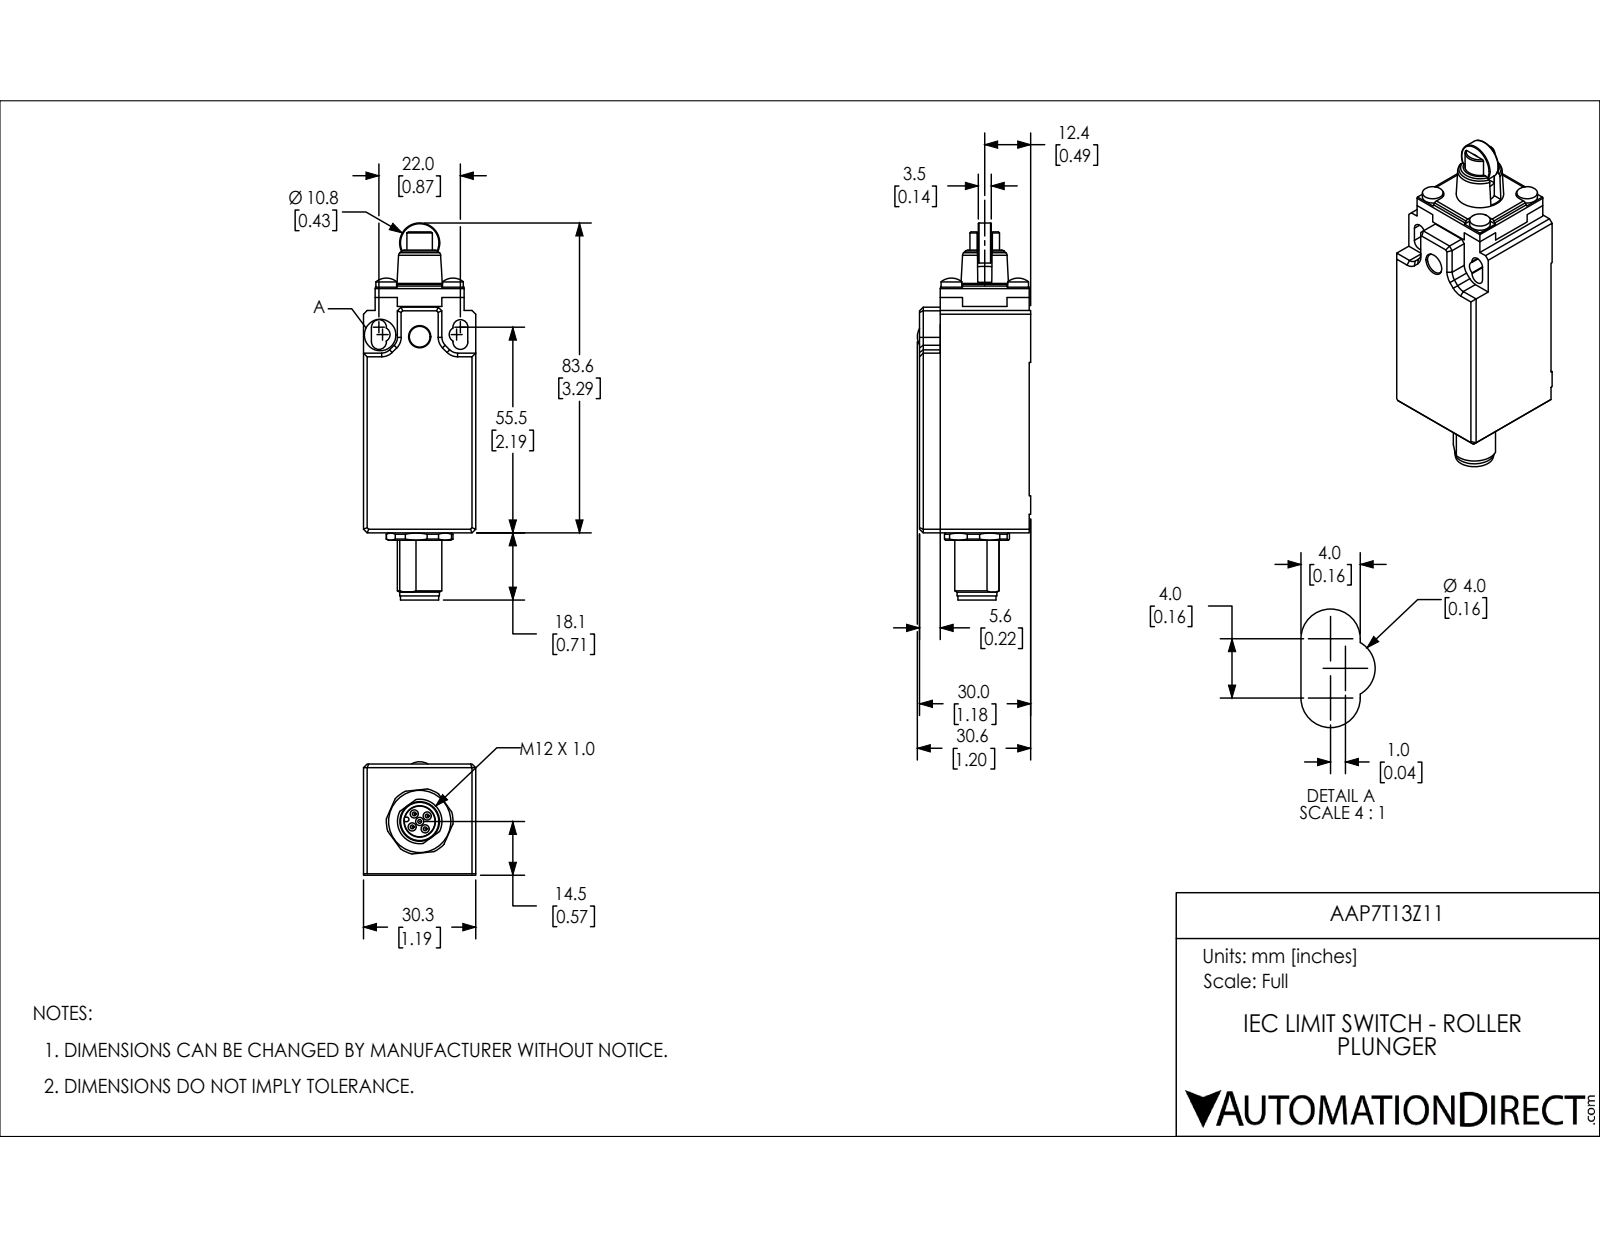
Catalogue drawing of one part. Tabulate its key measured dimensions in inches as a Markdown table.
| quantity | value |
| --- | --- |
| part name | AAP7T13Z11 |
| STEP written by | SolidWorks 2018 (AUTOMOTIVE_DESIGN) |
| units | inches |
| bodies | 5 solids, 328 faces (150 planar, 119 cylindrical, 59 other) |
| overall size | 4.004 × 1.205 × 1.193 |
| volume | 3.599 in³ |
| surface area | 25.07 in² |
| round holes (diameter × count) | 0.087 × 5, 0.236 × 1, 0.319 × 1, 0.512 × 1, 0.551 × 1, 0.63 × 1 |
| round bosses / shafts (diameter × count) | 0.22 × 6, 0.055 × 5, 0.039 × 5, 0.425 × 1, 0.421 × 1, 0.406 × 1, 0.315 × 1 |
| partial cylindrical surfaces (radius × count) | 0.039 × 8, 0.118 × 8, 0.079 × 6, 0.024 × 1, 0.236 × 1, 0.354 × 1, 0.394 × 1, 0.4 × 1 |
| main face-to-face distances | 1.193, 1.165, 2.406, 0.016, 1.181, 0.945, 0.236, 0.15, 0.039, 2.5 |
| hole center spacings | 0.098, 0.139, 0.197, 0.058, 0.083, 0.083, 0.161, 0.172 |
